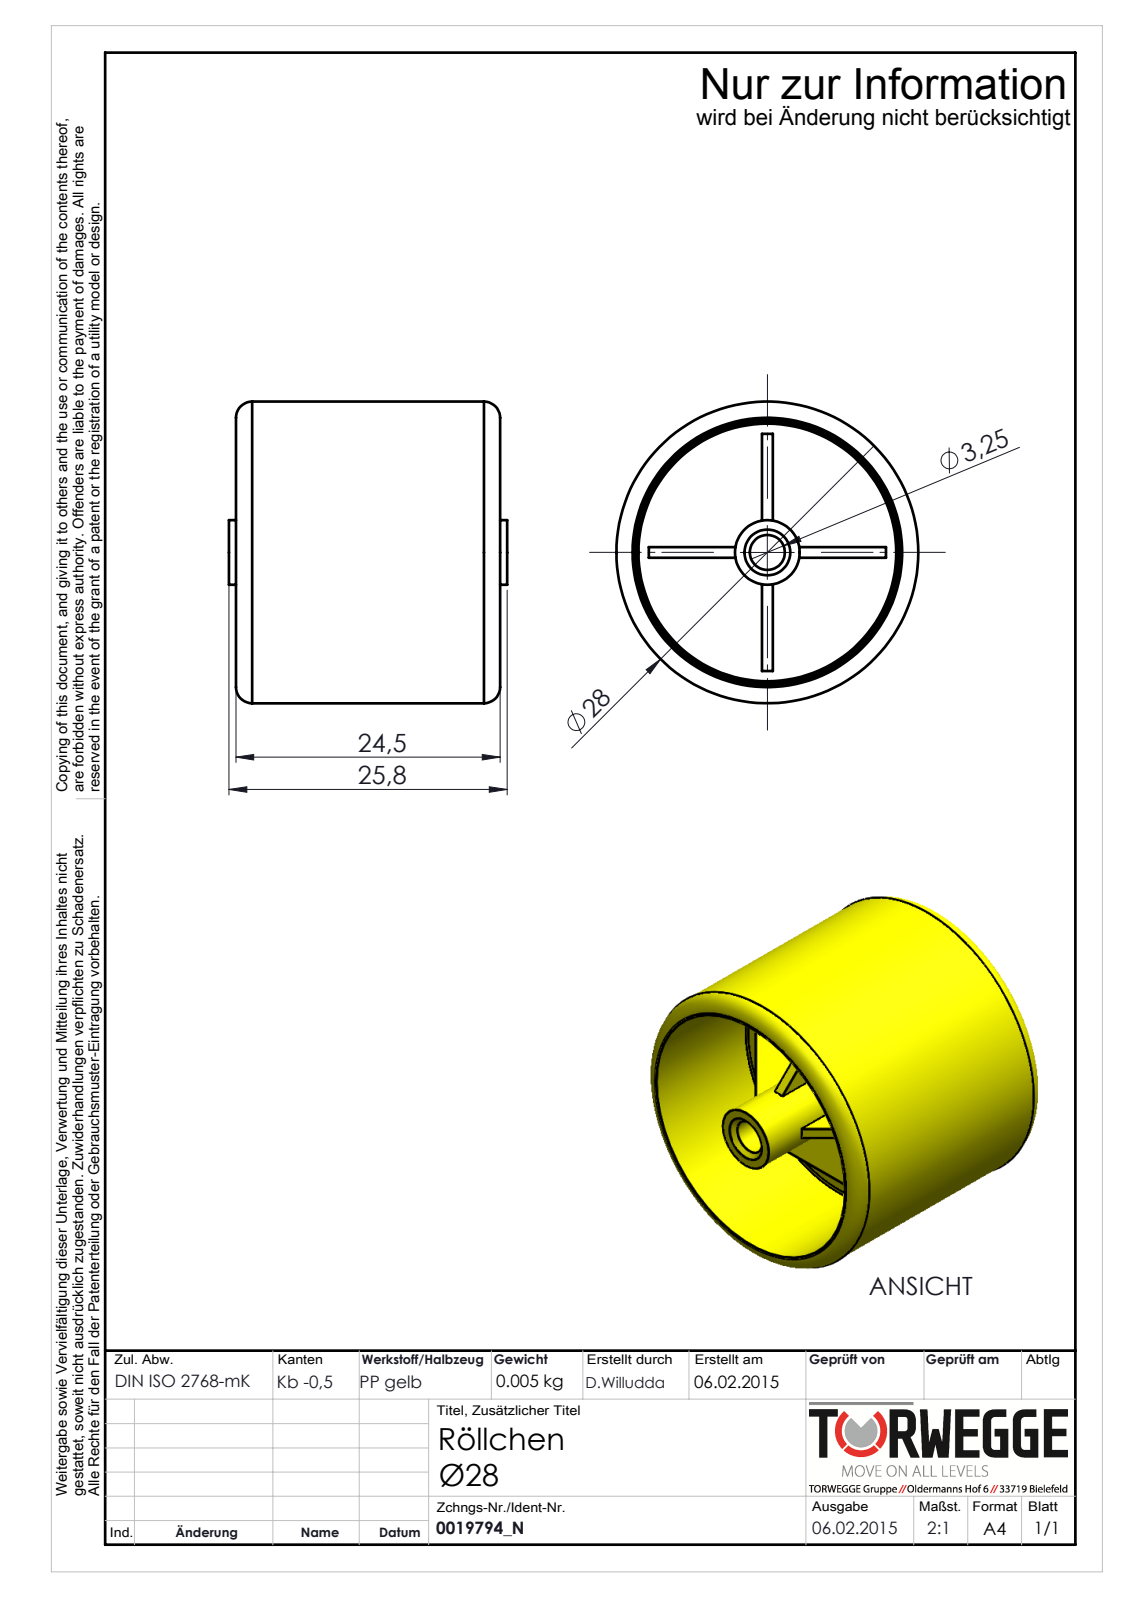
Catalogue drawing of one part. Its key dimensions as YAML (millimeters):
part_name: "0019794_N"
step_written_by: "SolidWorks 2014 (AUTOMOTIVE_DESIGN)"
units: millimeters
bodies: {solids: 1, faces: 54, planar: 30, cylindrical: 8, other: 16}
overall_size: [28, 28, 25.8]
volume: 4752
surface_area: 6206
round_holes:
  - {diameter: 3.25, count: 1}
round_bosses_or_shafts:
  - {diameter: 28, count: 1}
  - {diameter: 6, count: 1}
face_to_face_distances: [1.2, 1, 12.3, 13.5, 0.65, 25.15, 11.65, 12.85, 25.8, 24.5]
